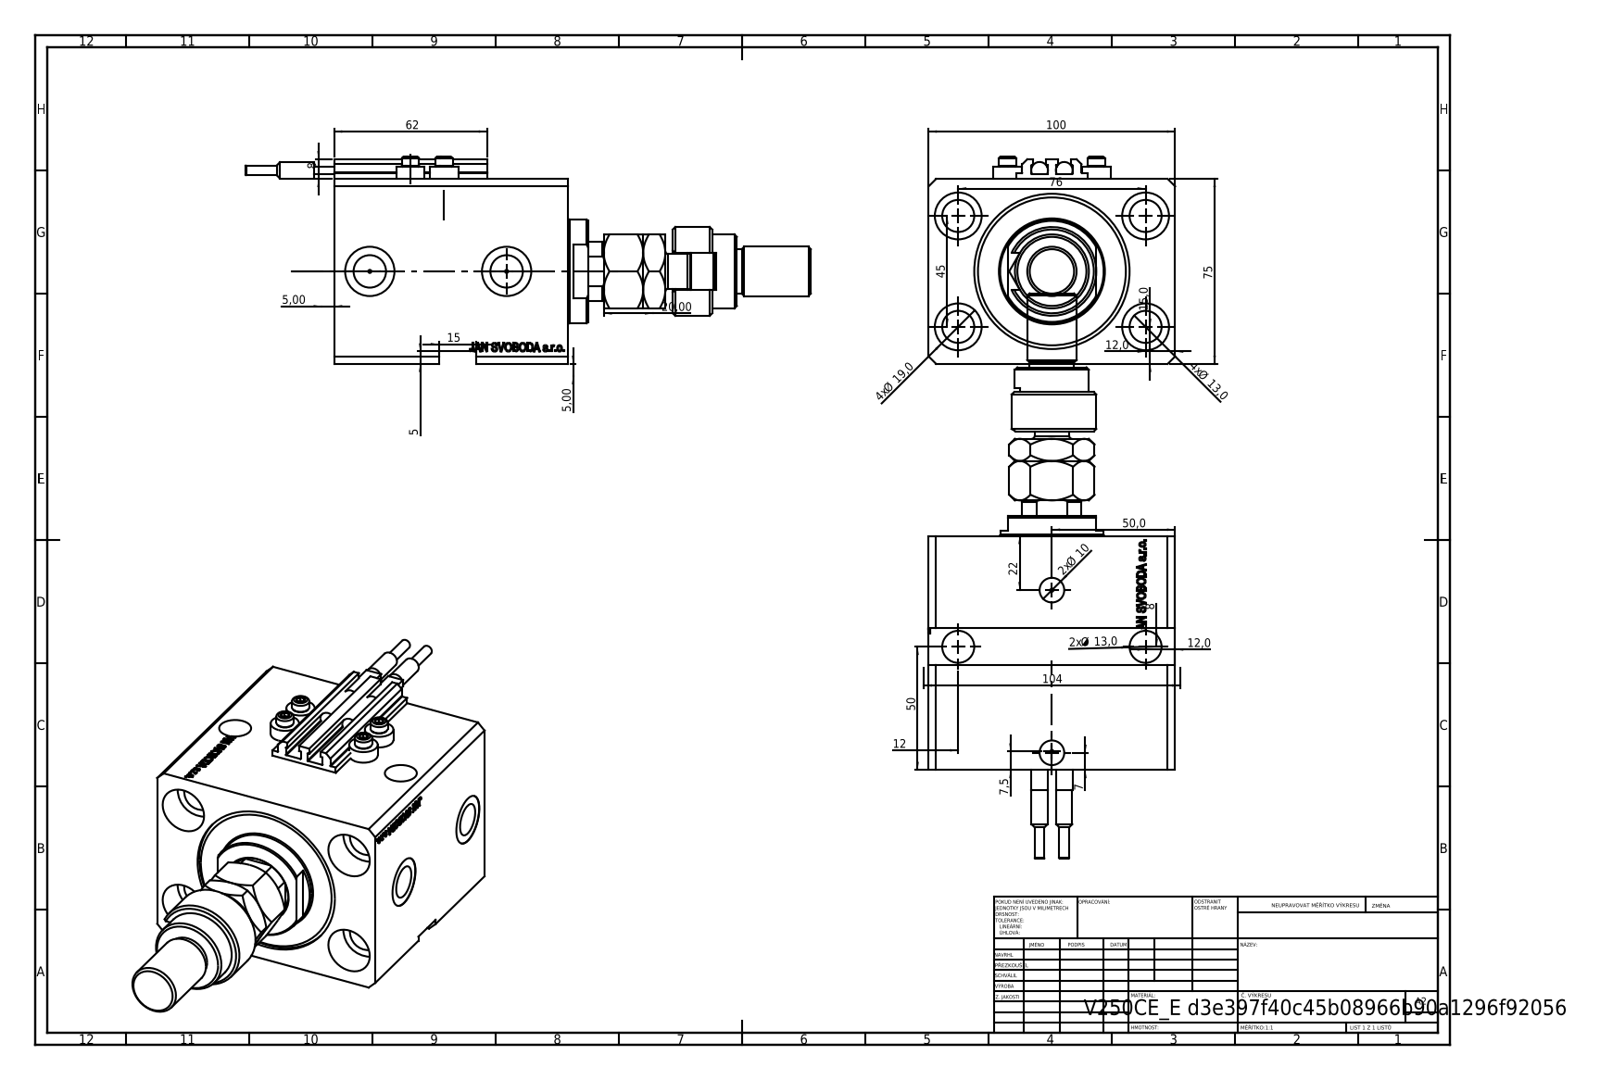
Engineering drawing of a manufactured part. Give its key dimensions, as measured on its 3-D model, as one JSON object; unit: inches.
{"part_name": "MFA; SWITCH_V250CE; V250CE_C_VCP; ALLEN BOLT V250CE (+3 more)", "step_written_by": "SolidWorks 2019 (CONFIG_CONTROL_DESIGN)", "units": "inches", "bodies": {"solids": 12, "faces": 1241, "planar": 599, "cylindrical": 163, "other": 479}, "overall_size": [9.031, 3.937, 3.307], "volume_in3": 40.06, "surface_area_in2": 217.3, "round_holes": [[0.512, 6], [0.049, 4], [0.157, 4], [0.748, 4], [0.394, 2], [0.518, 2], [0.787, 2], [0.728, 1], [1.102, 1], [1.969, 1], [2.48, 1]], "round_bosses_or_shafts": [[0.457, 4], [0.276, 4], [0.268, 2], [0.256, 2], [0.157, 2], [1.654, 1], [1.417, 1], [1.181, 1]], "partial_cylinders_radius": [[0.008, 10], [0.295, 1], [0.472, 1], [0.531, 1]], "face_to_face_distances": [2.953, 3.937, 3.74, 2.693, 0.469, 3.272, 2.224, 1.047, 0.197, 0.118], "hole_center_spacings": [1.739, 2.992, 0.535, 0.816, 1.086, 1.165, 1.181, 1.324]}
